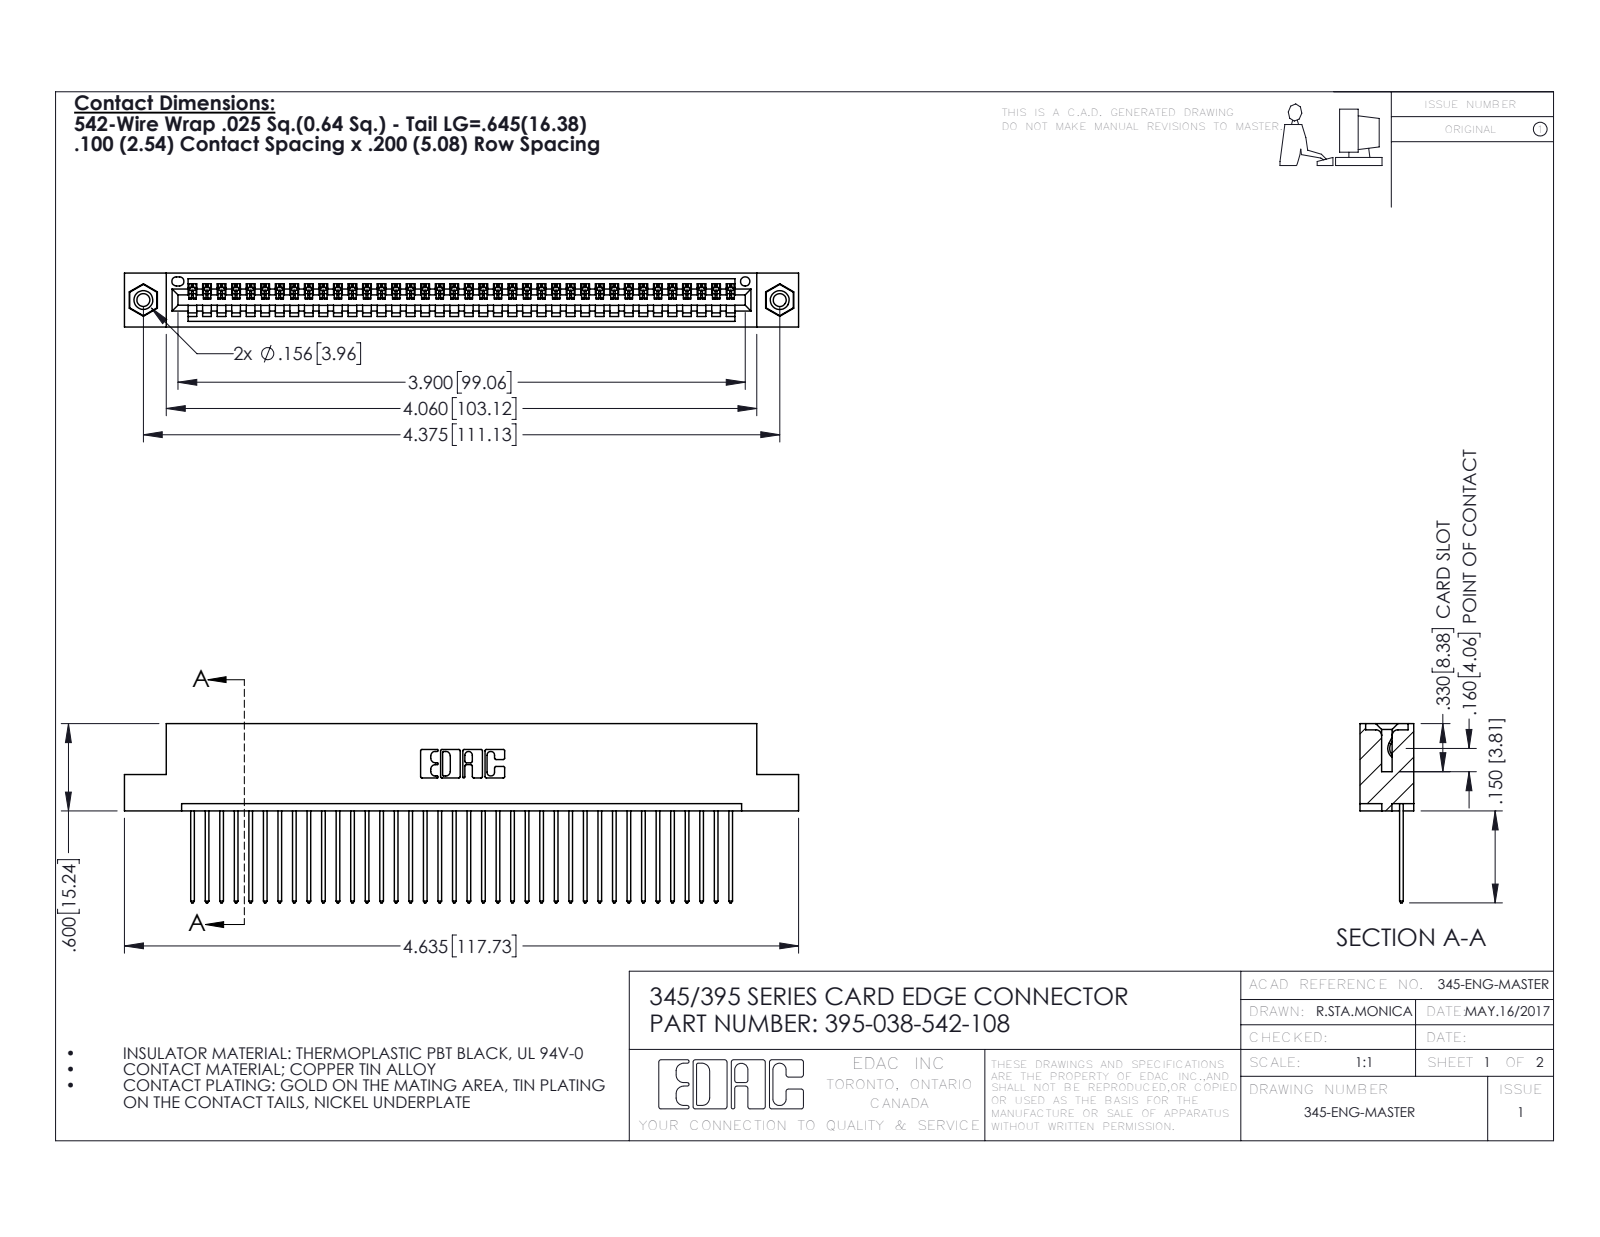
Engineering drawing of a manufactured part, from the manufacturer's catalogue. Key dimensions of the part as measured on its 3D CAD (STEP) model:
Part name (STEP PRODUCT): 395-038-542-108; 345 Part_Flush Mounting Lugs - 0.156 Dia-TI; 345-292-001_345-293-142; 345-250-001_345-250-003-102
STEP written by: SolidWorks 2016 (CONFIG_CONTROL_DESIGN)
Units: inches
Bodies: 41 solids, 2390 faces (1632 planar, 742 cylindrical, 16 other)
Overall size (bounding box): 4.635 × 1.232 × 0.37
Volume: 0.685 in³ · Surface area: 23.9 in²
Round holes (diameter × count): ⌀0.089 ×2, ⌀0.125 ×2, ⌀0.156 ×2, ⌀0.064 ×1
Round bosses / shafts (diameter × count): ⌀0.155 ×2
Partial cylindrical surfaces — rounded edges, fillets, slot ends (radius × count): R0.006 ×76, R0.01 ×76, R0.01 ×22, R0.007 ×6, R0.031 ×6, R0.026 ×3, R0.031 ×2, R0.04 ×2
Main face-to-face distances: 0.072, 0.298, 0.37, 0.2, 0.098, 0.272, 0.025, 0.225, 0.149, 0.072
Hole centre spacings: 0.27, 4.139, 4.375
